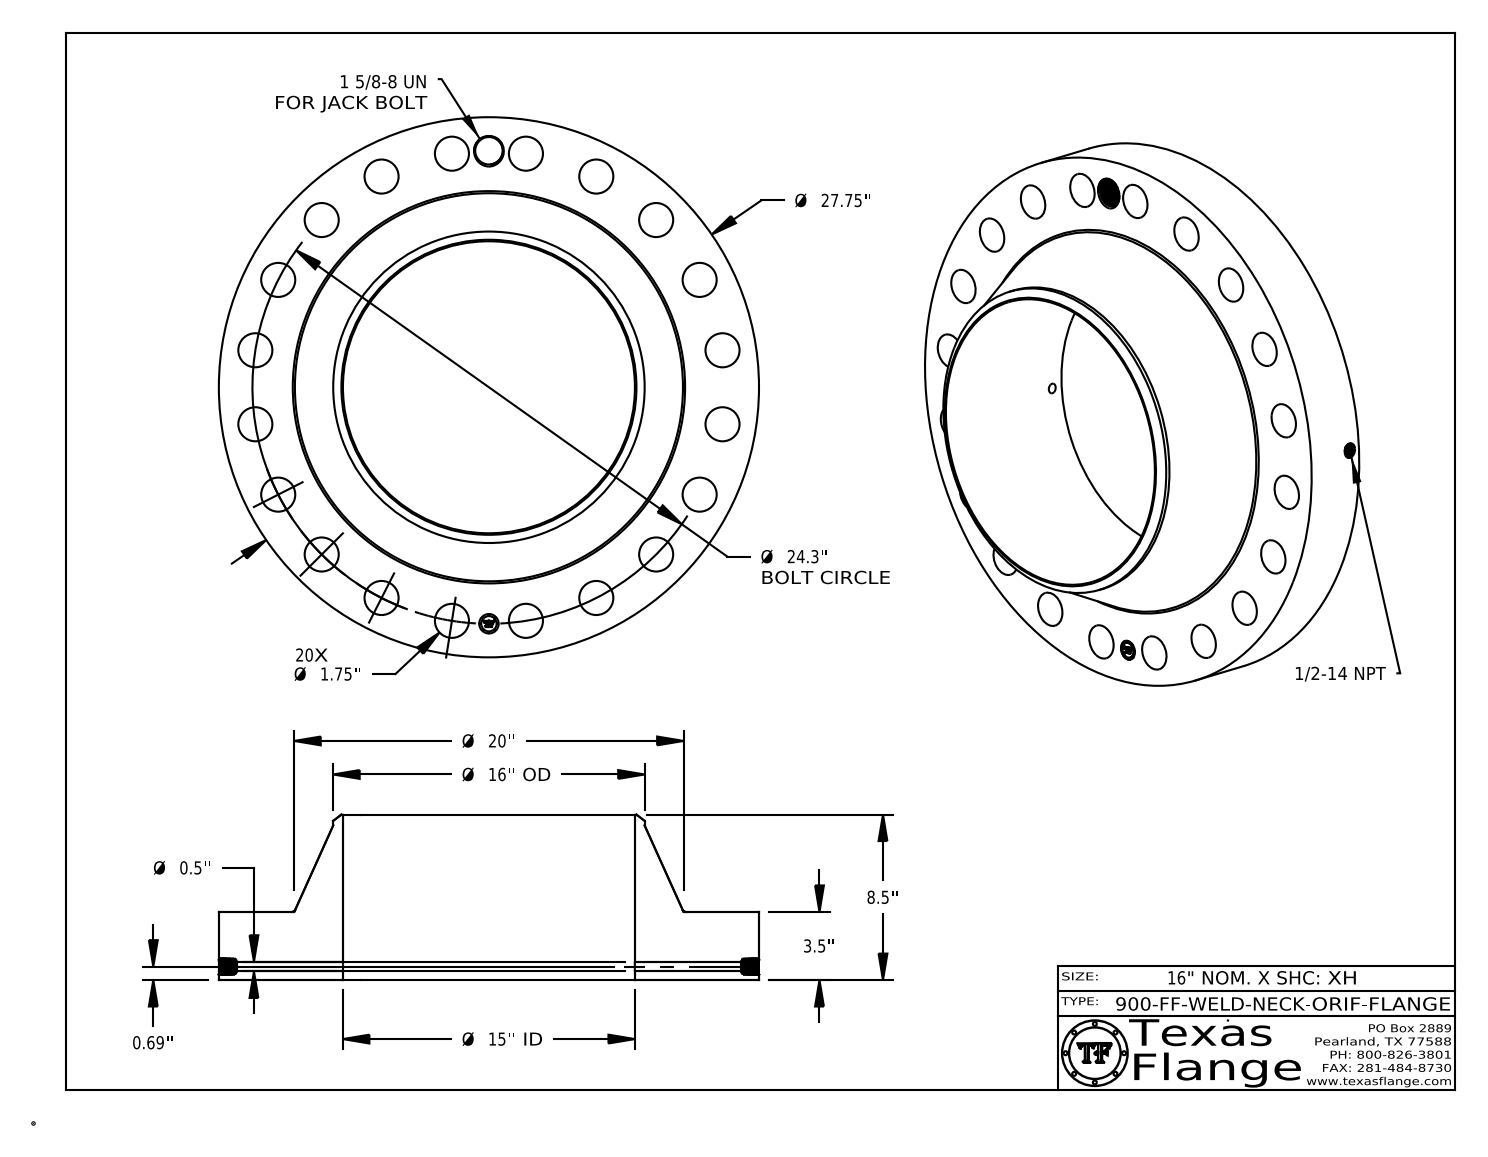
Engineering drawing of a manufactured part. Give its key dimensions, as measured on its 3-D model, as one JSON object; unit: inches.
{"part_name": "900-FF-WELD-NECK", "step_written_by": "CATIA V5 STEP AP214 (AUTOMOTIVE_DESIGN)", "units": "inches", "bodies": {"solids": 1, "faces": 868, "planar": 368, "cylindrical": 141, "other": 359}, "overall_size": [27.75, 27.75, 8.5], "volume_in3": 1681, "surface_area_in2": 2082, "round_holes": [[1.75, 20], [0.5, 1], [0.672, 1], [1, 1], [1.409, 1], [15, 1]], "round_bosses_or_shafts": [[0.061, 8], [27.75, 1], [16, 1], [0.788, 1]], "face_to_face_distances": [3.5, 8.5, 5, 3.485, 0.015, 5.015, 0.298, 0.293, 0.054, 0.248], "hole_center_spacings": [12.15, 17.183, 19.659, 23.111, 24.001, 21.652, 3.802, 14.283]}
